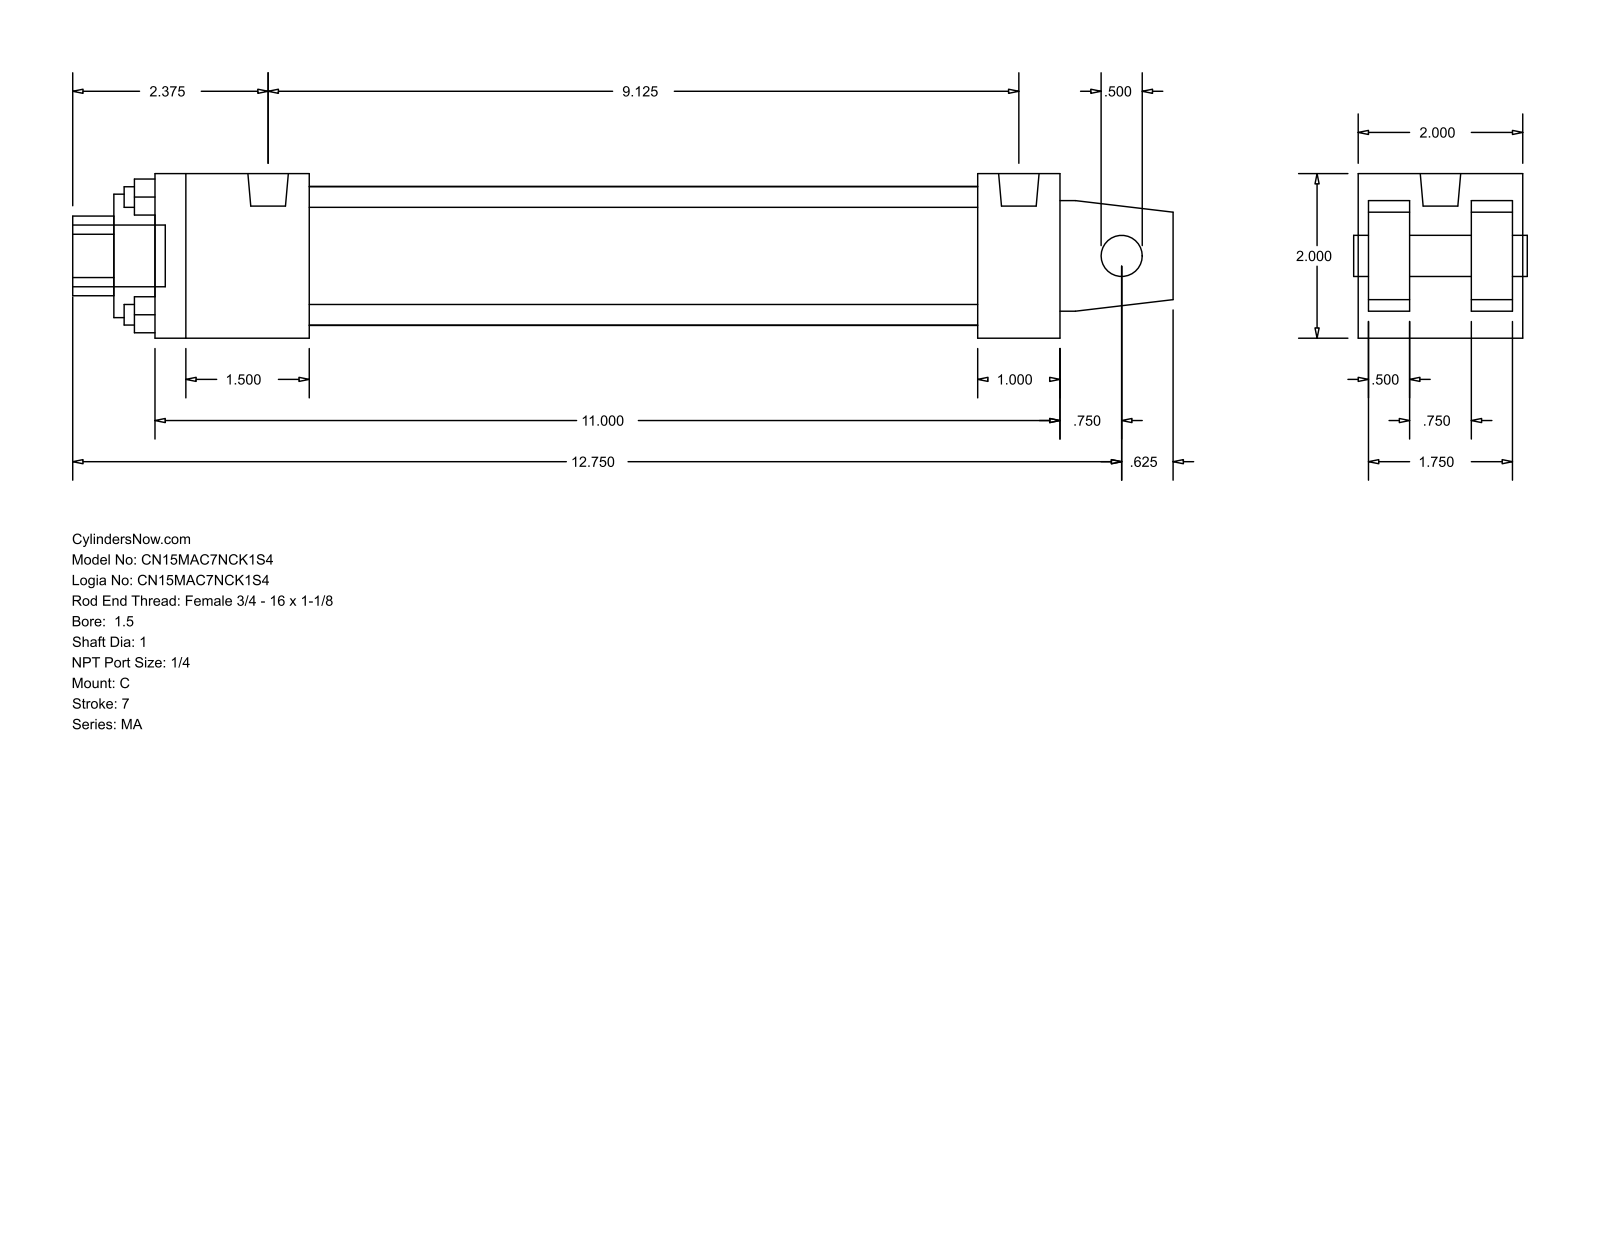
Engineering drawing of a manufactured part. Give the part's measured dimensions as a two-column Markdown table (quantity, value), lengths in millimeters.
| quantity | value |
| --- | --- |
| part name | MA_C__0150_1 |
| STEP written by | GSSL Pune (CONFIG_CONTROL_DESIGN) |
| units | millimeters |
| bodies | 0 solids, 103 faces (76 planar, 27 cylindrical, 0 other) |
| overall size | 339.73 × 50.8 × 50.8 |
| round holes (diameter × count) | 6.35 × 4, 12.7 × 1, 25.4 × 1, 38.1 × 1, 42.93 × 1 |
| round bosses / shafts (diameter × count) | 7.94 × 4, 12.49 × 2, 19.05 × 1 |
| partial cylindrical surfaces (radius × count) | 12.29 × 1 |
| main face-to-face distances | 50.8, 47.63, 12.7, 34.93, 3.17, 15.87, 31.76, 60.33, 266.7, 44.46 |
| hole center spacings | 25.68, 36.32, 51.36 |
